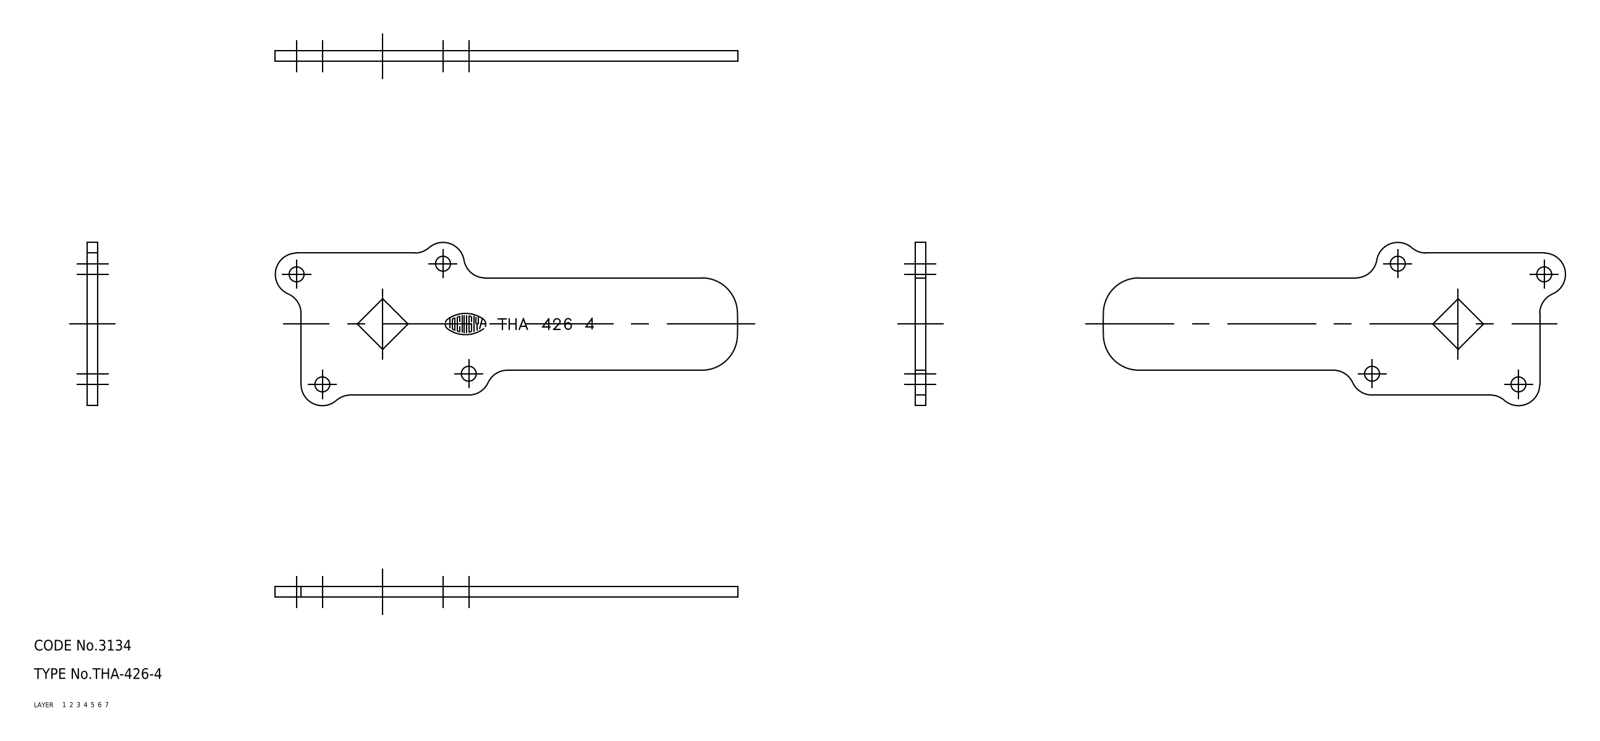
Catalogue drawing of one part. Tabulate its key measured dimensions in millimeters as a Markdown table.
| quantity | value |
| --- | --- |
| part name | cam |
| STEP written by | CADfix (AUTOMOTIVE_DESIGN) |
| units | millimeters |
| bodies | 1 solid, 31 faces (0 planar, 0 cylindrical, 31 other) |
| overall size | 130.25 × 46 × 3 |
| volume | 11 443 mm³ |
| surface area | 8 871 mm² |
